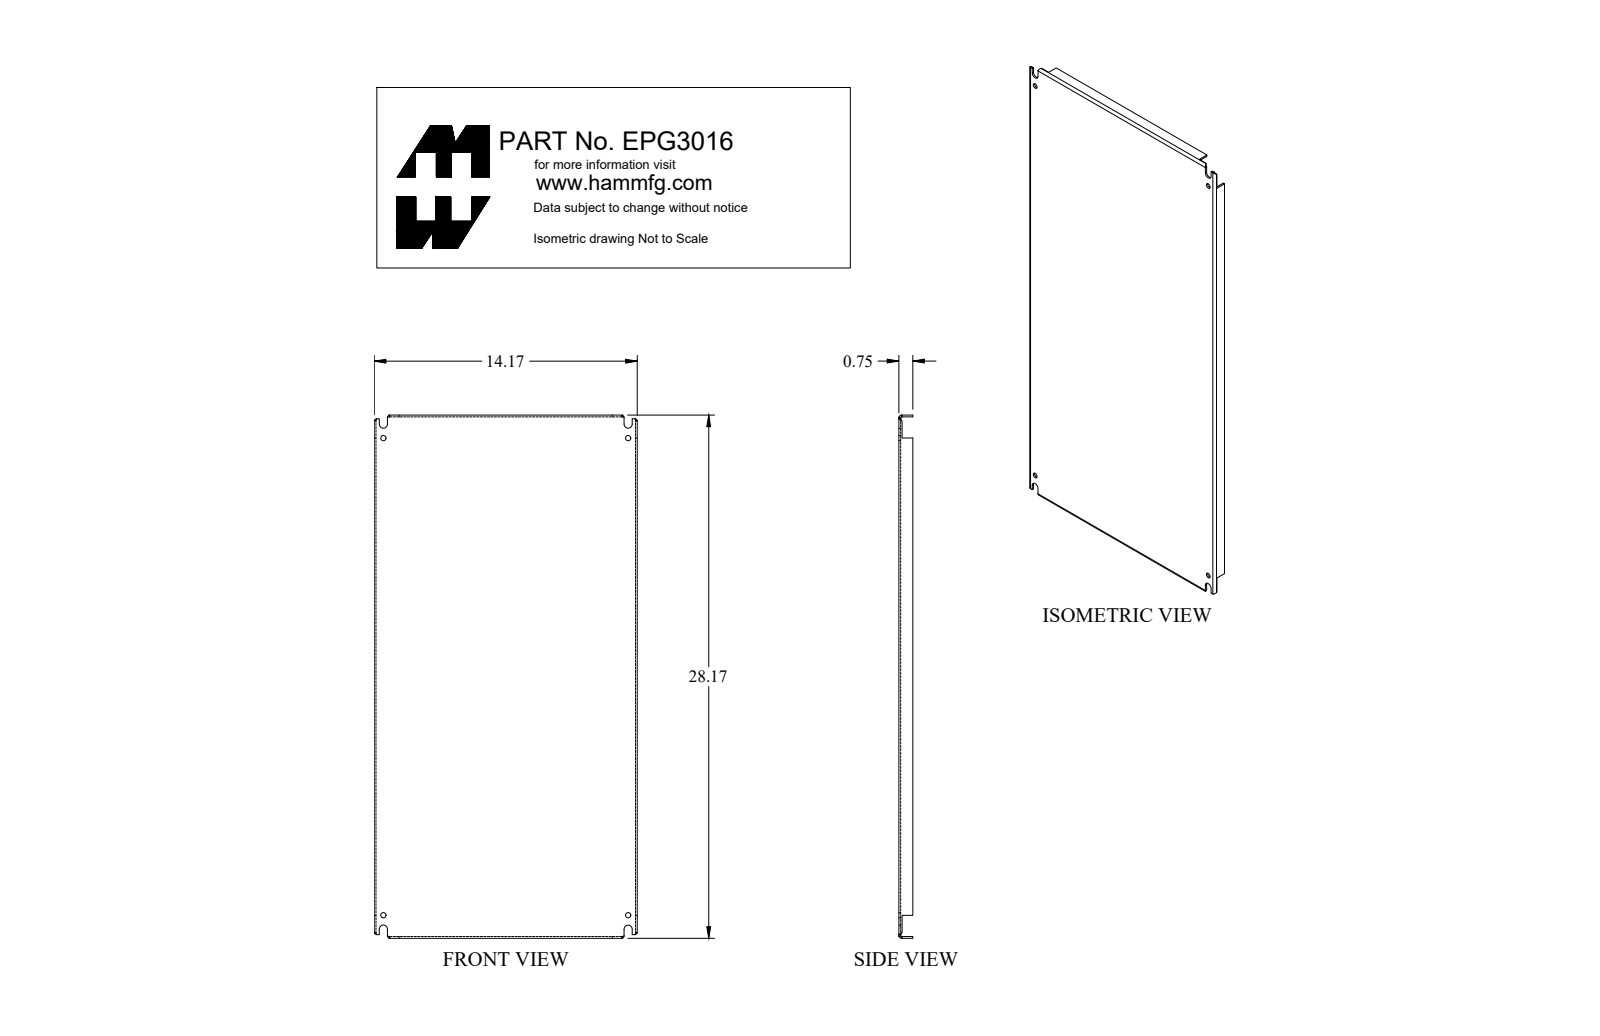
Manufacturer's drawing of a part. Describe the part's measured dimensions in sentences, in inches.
The part is named "EPG3016". Its 3-D file was written by "SolidWorks 2018 (AUTOMOTIVE_DESIGN)". It is 1 solid with 128 faces: 74 planar, 38 cylindrical and 16 other. Overall it measures 28.17 by 14.17 by 0.75 inches. Its volume is 42.11 cubic inches and its surface area 895.6 square inches. Round holes: 4 of diameter 0.281. Partial cylindrical surfaces (rounded edges, fillets, slot ends): 4 of radius 0.048, 4 of radius 0.063, 4 of radius 0.143, 4 of radius 0.219. The main face-to-face distances are 0.095, 14.075, 13.98, 14.17, 28.075, 27.98, 28.17, 0.75, 0.655, 0.171. The hole center spacings are 13.188, 25.688, 28.876.
